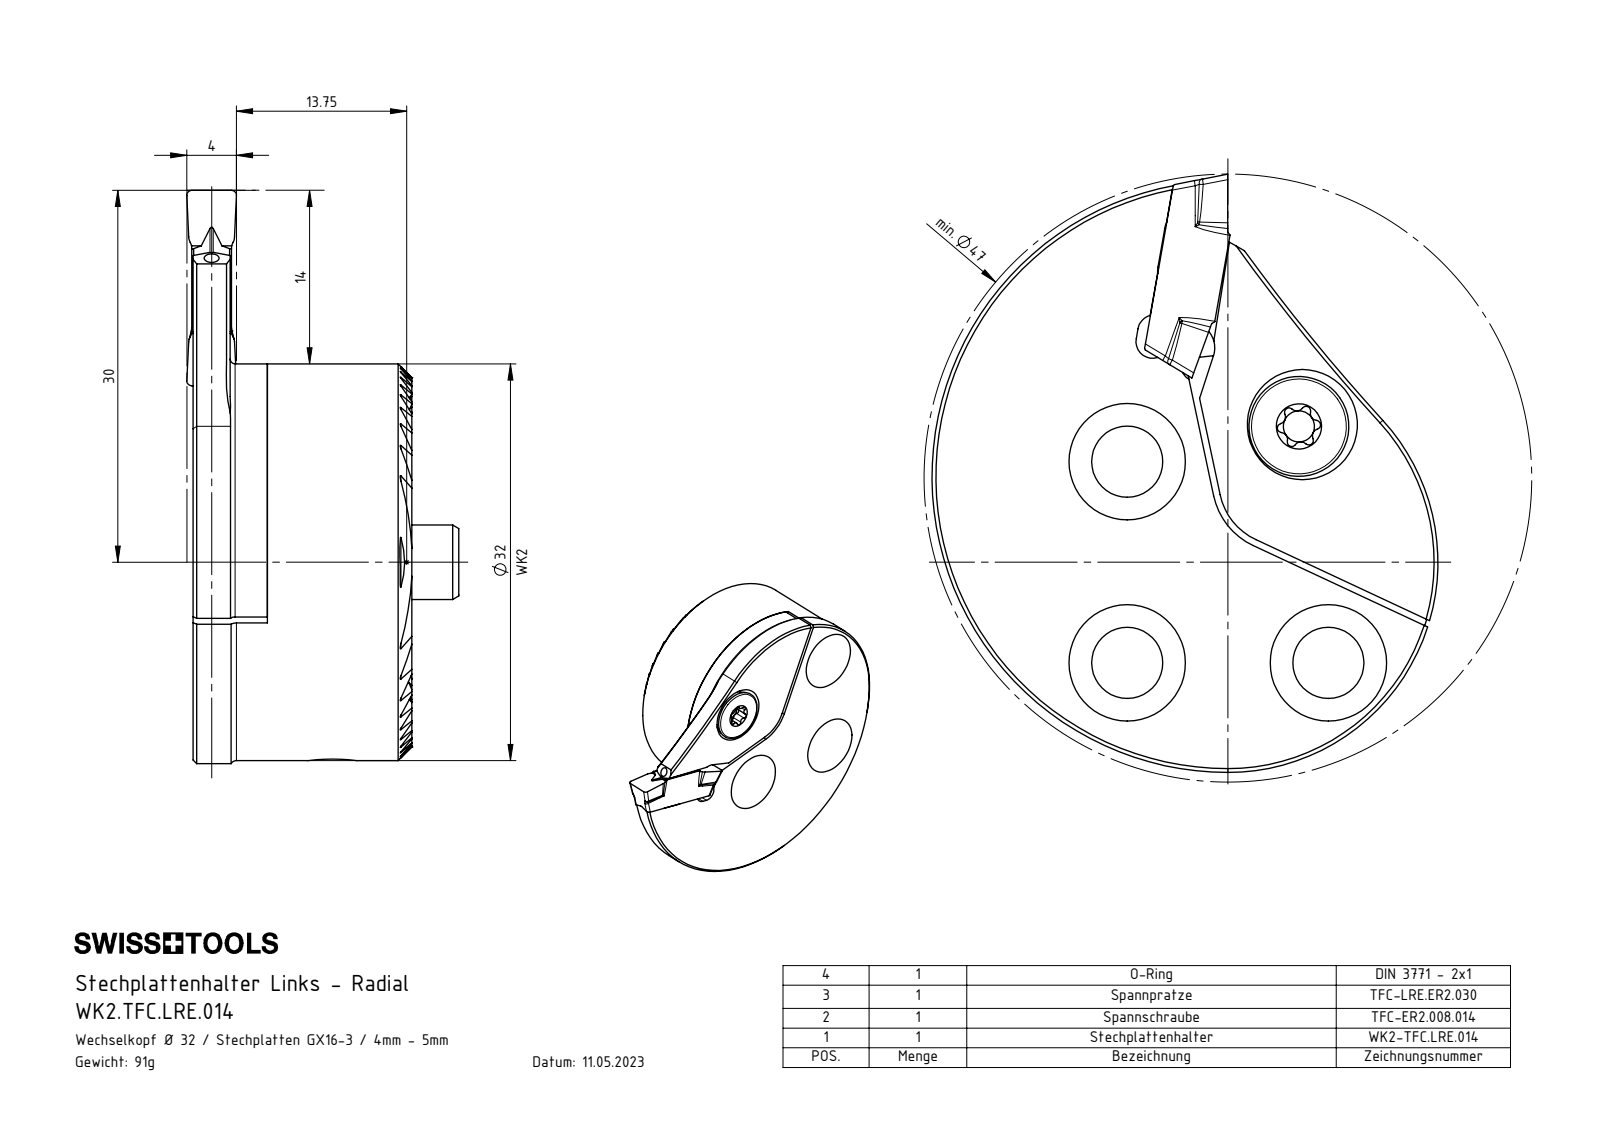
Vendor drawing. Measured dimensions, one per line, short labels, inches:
name: KVT_MB_600_040; WK2.TFC.LRE.014; DIN 6325_ø4x10_2x6; DIN 3771 - 2x1 (+6 more)
written by: SolidWorks 2022 (AUTOMOTIVE_DESIGN)
unit: in
bodies: 9 solids, 530 faces (208 planar, 193 cylindrical, 129 other)
size: 1.821 × 1.54 × 0.884
volume: 0.732 in³; area: 13.4 in²
holes: 4× ⌀0.217, 3× ⌀0.354, 2× ⌀0.047, 2× ⌀0.157, 2× ⌀0.165, 1× ⌀0.094, 1× ⌀0.098, 1× ⌀0.118, 1× ⌀0.13, 1× ⌀0.256, 1× ⌀0.472
bosses: 1× ⌀1.26, 1× ⌀0.472, 1× ⌀0.236, 1× ⌀0.197, 1× ⌀0.161, 1× ⌀0.157
rounds: 22× R0.005, 6× R0.014, 6× R0.016, 6× R0.021, 4× R0.091, 3× R0.051, 1× R0.079, 1× R0.197
face distances: 0.118, 0.051, 0.102, 0.236, 0.154, 0.256, 0.205, 0.511, 0.46, 0.409
hole spacings: 0.433, 0.613, 0.217, 0.224, 0.353, 0.381, 0.384, 0.467
